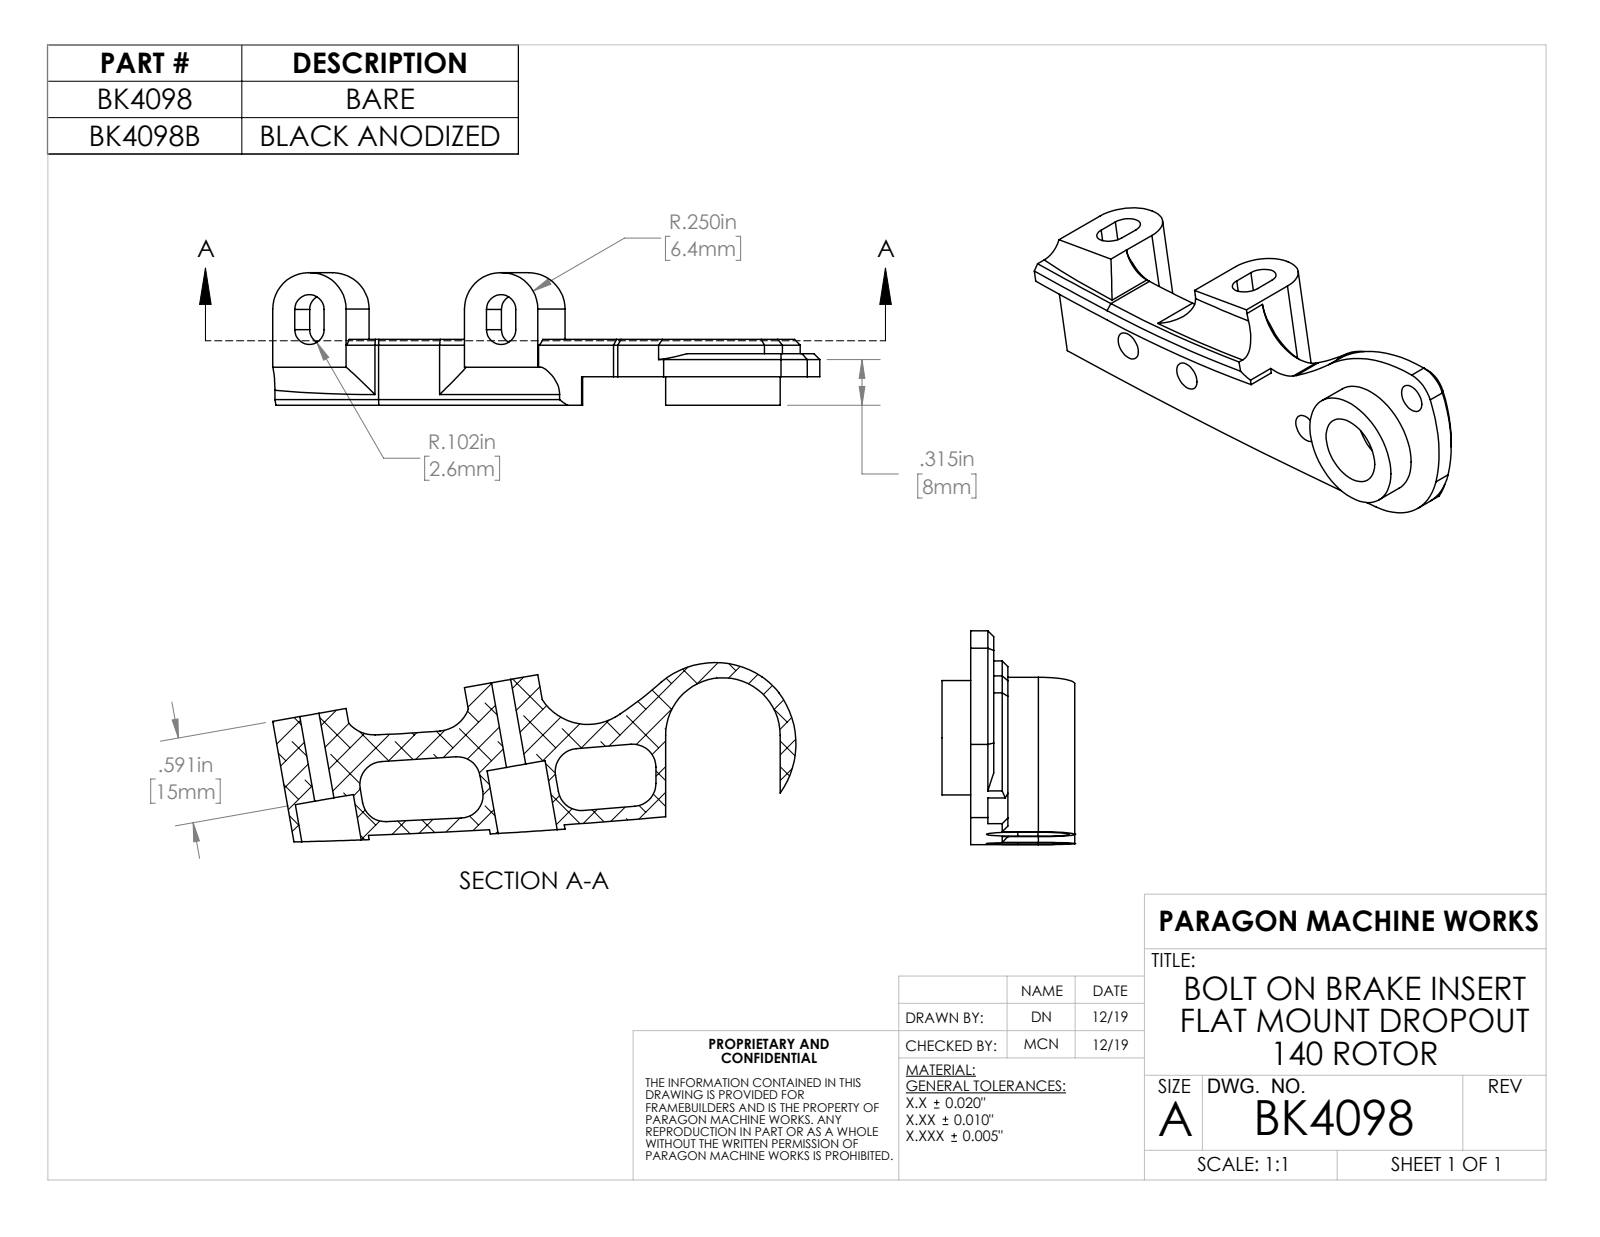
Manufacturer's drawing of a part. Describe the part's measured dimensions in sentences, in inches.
The part is named "BK4098". Its 3-D file was written by "SolidWorks 2020 (AUTOMOTIVE_DESIGN)". It is 1 solid with 110 faces: 37 planar, 50 cylindrical and 23 other. Overall it measures 3.76 by 1.469 by 0.911 inches. Its volume is 0.928 cubic inches and its surface area 15.43 square inches. Round holes: 4 of diameter 0.197, 1 of diameter 0.472. Round bosses or shafts: 1 of diameter 0.787. Partial cylindrical surfaces (rounded edges, fillets, slot ends): 8 of radius 0.157, 4 of radius 0.102, 4 of radius 0.217, 4 of radius 0.25, 3 of radius 0.197, 1 of radius 0.344, 1 of radius 0.512, 1 of radius 0.607. The main face-to-face distances are 0.157, 0.098, 0.256, 0.039, 1.339, 0.138, 0.118, 0.453, 0.354, 0.315. The hole center spacings are 0.669, 0.571, 1.166, 1.282, 1.736, 1.823, 2.365, 2.39.
